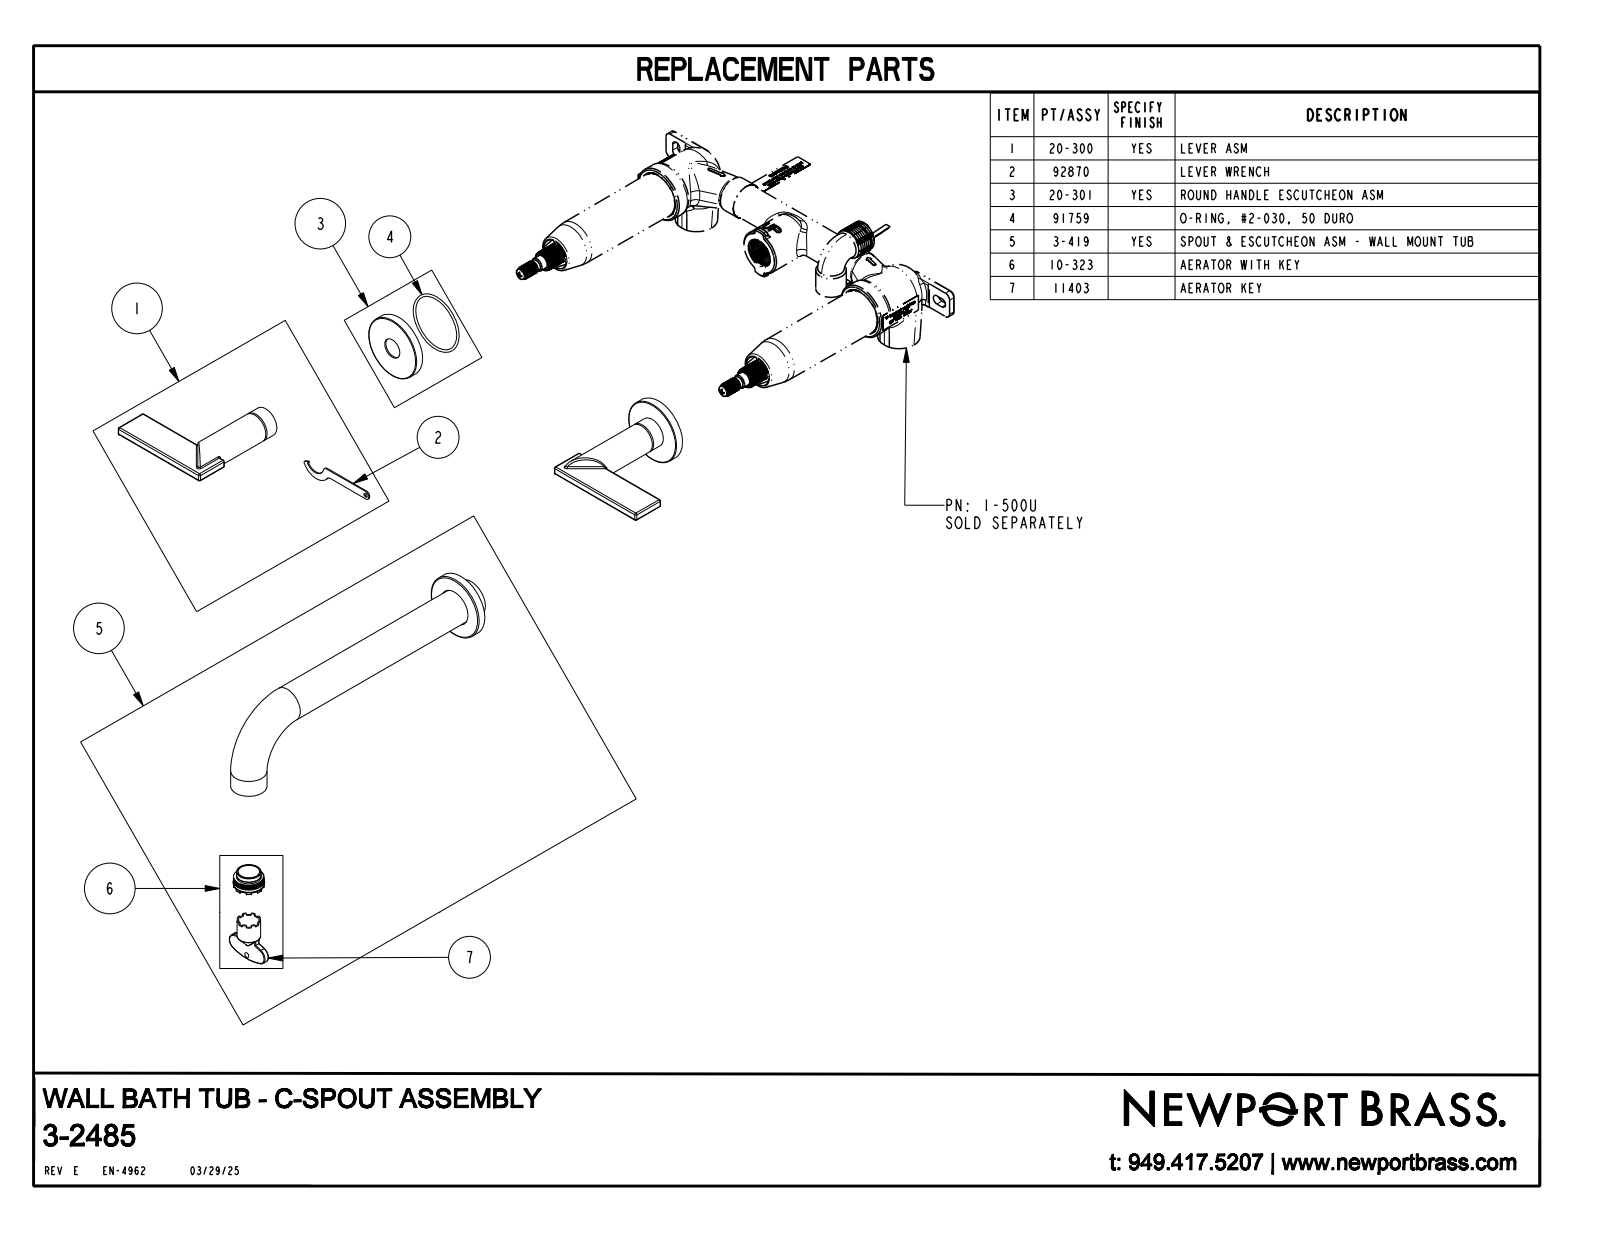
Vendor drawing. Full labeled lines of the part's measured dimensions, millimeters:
Part name (STEP PRODUCT): 3-2485_SW0001
STEP written by: CREO PARAMETRIC BY PTC INC, 2018400 (AUTOMOTIVE_DESIGN)
Units: millimetres
Bodies: 3 solids, 139 faces (29 planar, 58 cylindrical, 52 other)
Overall size (bounding box): 330.1 × 226.7 × 222.3
Volume: 224 700 mm³ · Surface area: 50 430 mm²
Round bosses / shafts (diameter × count): ⌀47 ×3, ⌀25.4 ×2, ⌀21.8 ×2, ⌀17.3 ×2
Partial cylindrical surfaces — rounded edges, fillets, slot ends (radius × count): R1 ×28
Main face-to-face distances: 6.4, 6, 87.6, 81.3, 200.2, 206.2, 62.6, 56.3, 25, 17.2
